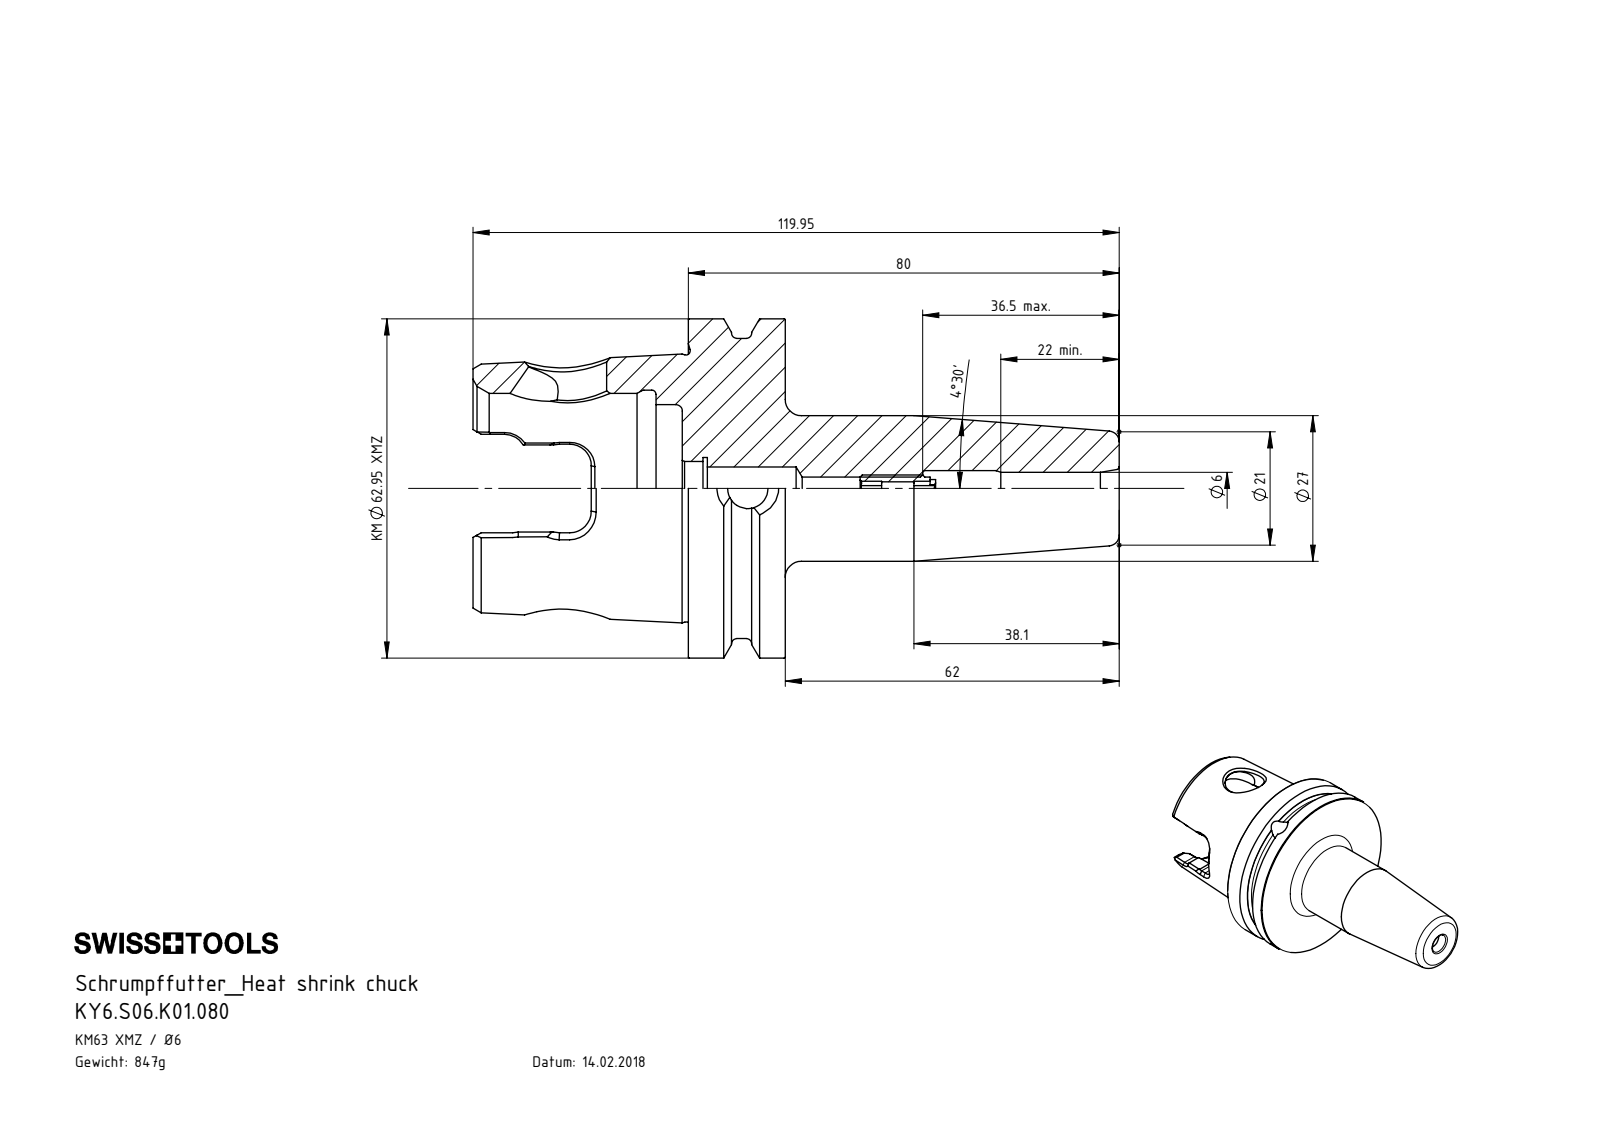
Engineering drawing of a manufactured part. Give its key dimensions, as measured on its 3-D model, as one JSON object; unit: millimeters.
{"part_name": "KY6-S06.K01.080; ERU-AN1.K01.014_A; KY6-S06.K01.080_A", "step_written_by": "SolidWorks 2012 (CONFIG_CONTROL_DESIGN)", "units": "millimeters", "bodies": {"solids": 2, "faces": 274, "planar": 79, "cylindrical": 60, "other": 135}, "overall_size": [119.95, 62.95, 62.95], "volume_mm3": 107924, "surface_area_mm2": 26149, "round_holes": [[7.47, 2], [2.5, 1], [4.2, 1], [6, 1], [6.6, 1], [8, 1], [8.48, 1], [10, 1], [11.5, 1], [14.5, 1], [31.1, 1], [35.27, 1]], "round_bosses_or_shafts": [[62.95, 1], [55.7, 1], [27, 1], [5, 1]], "partial_cylinders_radius": [[4, 6], [7.04, 2]], "face_to_face_distances": [18, 1.1, 19.1, 6, 4.9, 24, 39.95, 86, 81.1, 80]}
